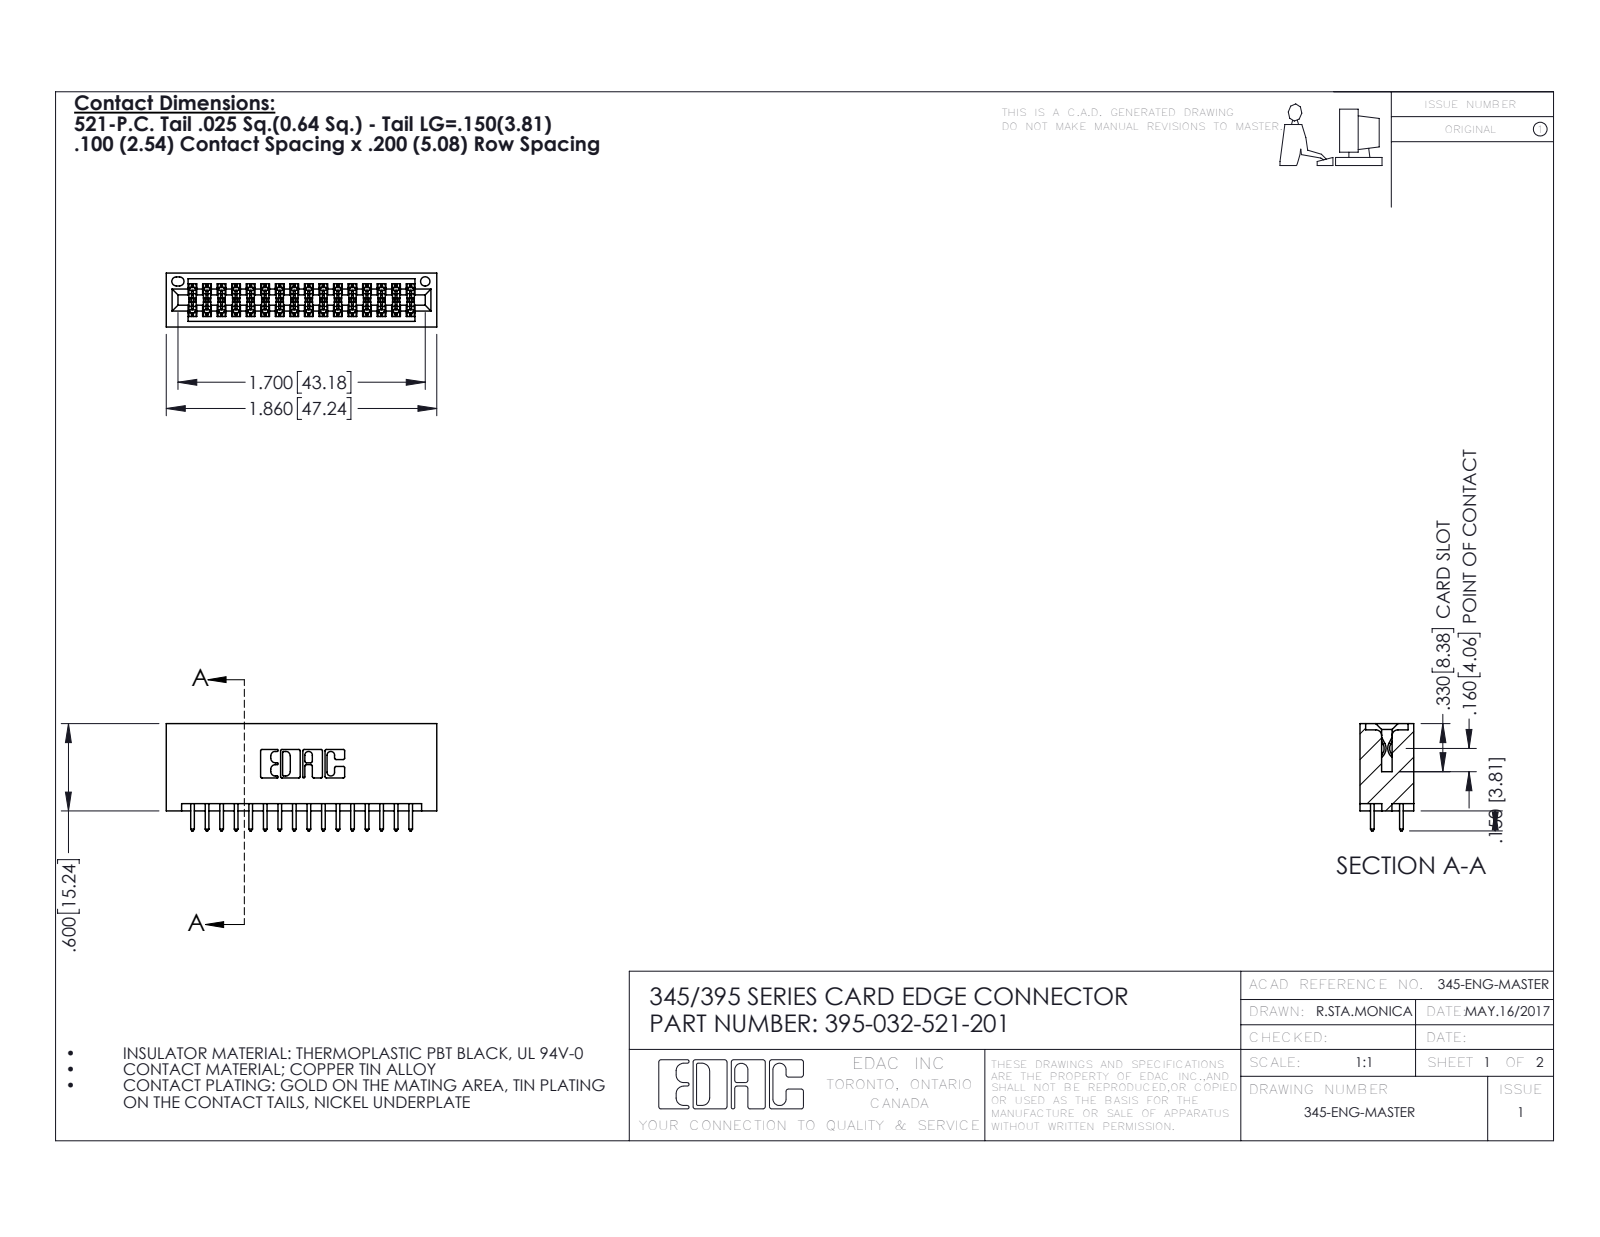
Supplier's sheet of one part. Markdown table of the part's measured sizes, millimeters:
| quantity | value |
| --- | --- |
| part name | 345-292-001_345-293-121; 395-032-521-201; 345 Part_No Mounting Lugs |
| STEP written by | SolidWorks 2016 (CONFIG_CONTROL_DESIGN) |
| units | millimeters |
| bodies | 33 solids, 1718 faces (1132 planar, 586 cylindrical, 0 other) |
| overall size | 47.2 × 18.7 × 9.4 |
| volume | 4 950 mm³ |
| surface area | 7 032 mm² |
| round holes (diameter × count) | 1.6 × 1 |
| partial cylindrical surfaces (radius × count) | 0.2 × 48, 0.3 × 32, 0.3 × 22, 0.2 × 6, 0.8 × 6, 0.7 × 3, 0.4 × 2, 0.5 × 2 |
| main face-to-face distances | 7.6, 1.8, 5.1, 9.4, 2.5, 6.9, 0.6, 5.7, 2.5, 4.4 |
